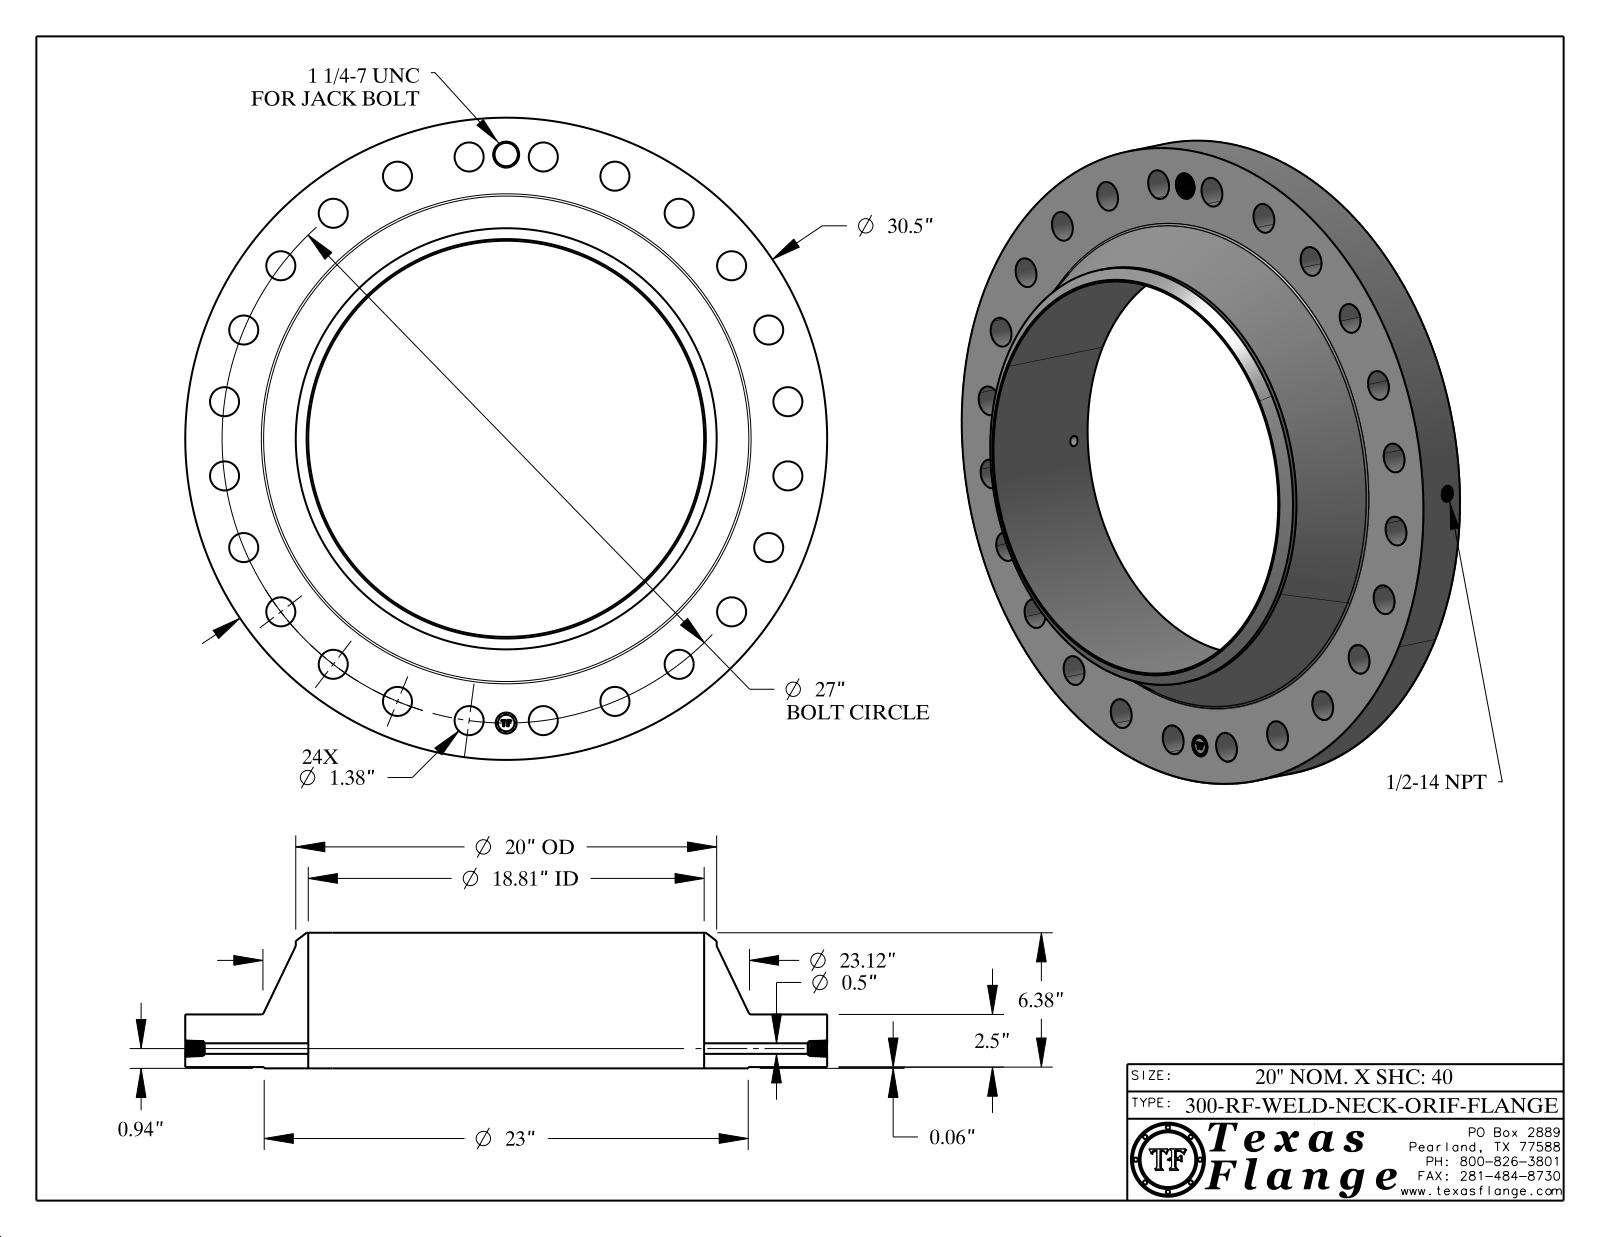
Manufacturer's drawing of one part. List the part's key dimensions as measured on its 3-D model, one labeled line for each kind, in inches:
Part name (STEP PRODUCT): 300-RF-WELD-NECK
STEP written by: CATIA V5 STEP AP214 (AUTOMOTIVE_DESIGN)
Units: inches
Bodies: 1 solid, 818 faces (369 planar, 131 cylindrical, 318 other)
Overall size (bounding box): 30.5 × 30.5 × 6.44
Volume: 1 347 in³ · Surface area: 1 911 in²
Round holes (diameter × count): ⌀1.38 ×24, ⌀0.5 ×1, ⌀0.672 ×1, ⌀1 ×1, ⌀1.109 ×1, ⌀18.812 ×1
Round bosses / shafts (diameter × count): ⌀0.061 ×8, ⌀30.5 ×1, ⌀23 ×1, ⌀20 ×1, ⌀0.788 ×1
Main face-to-face distances: 2.5, 0.06, 2.56, 6.44, 6.38, 3.88, 2.545, 2.485, 0.015, 3.895
Hole centre spacings: 13.5, 23.383, 24.945, 21.42, 3.524, 6.988, 19.092, 26.08
